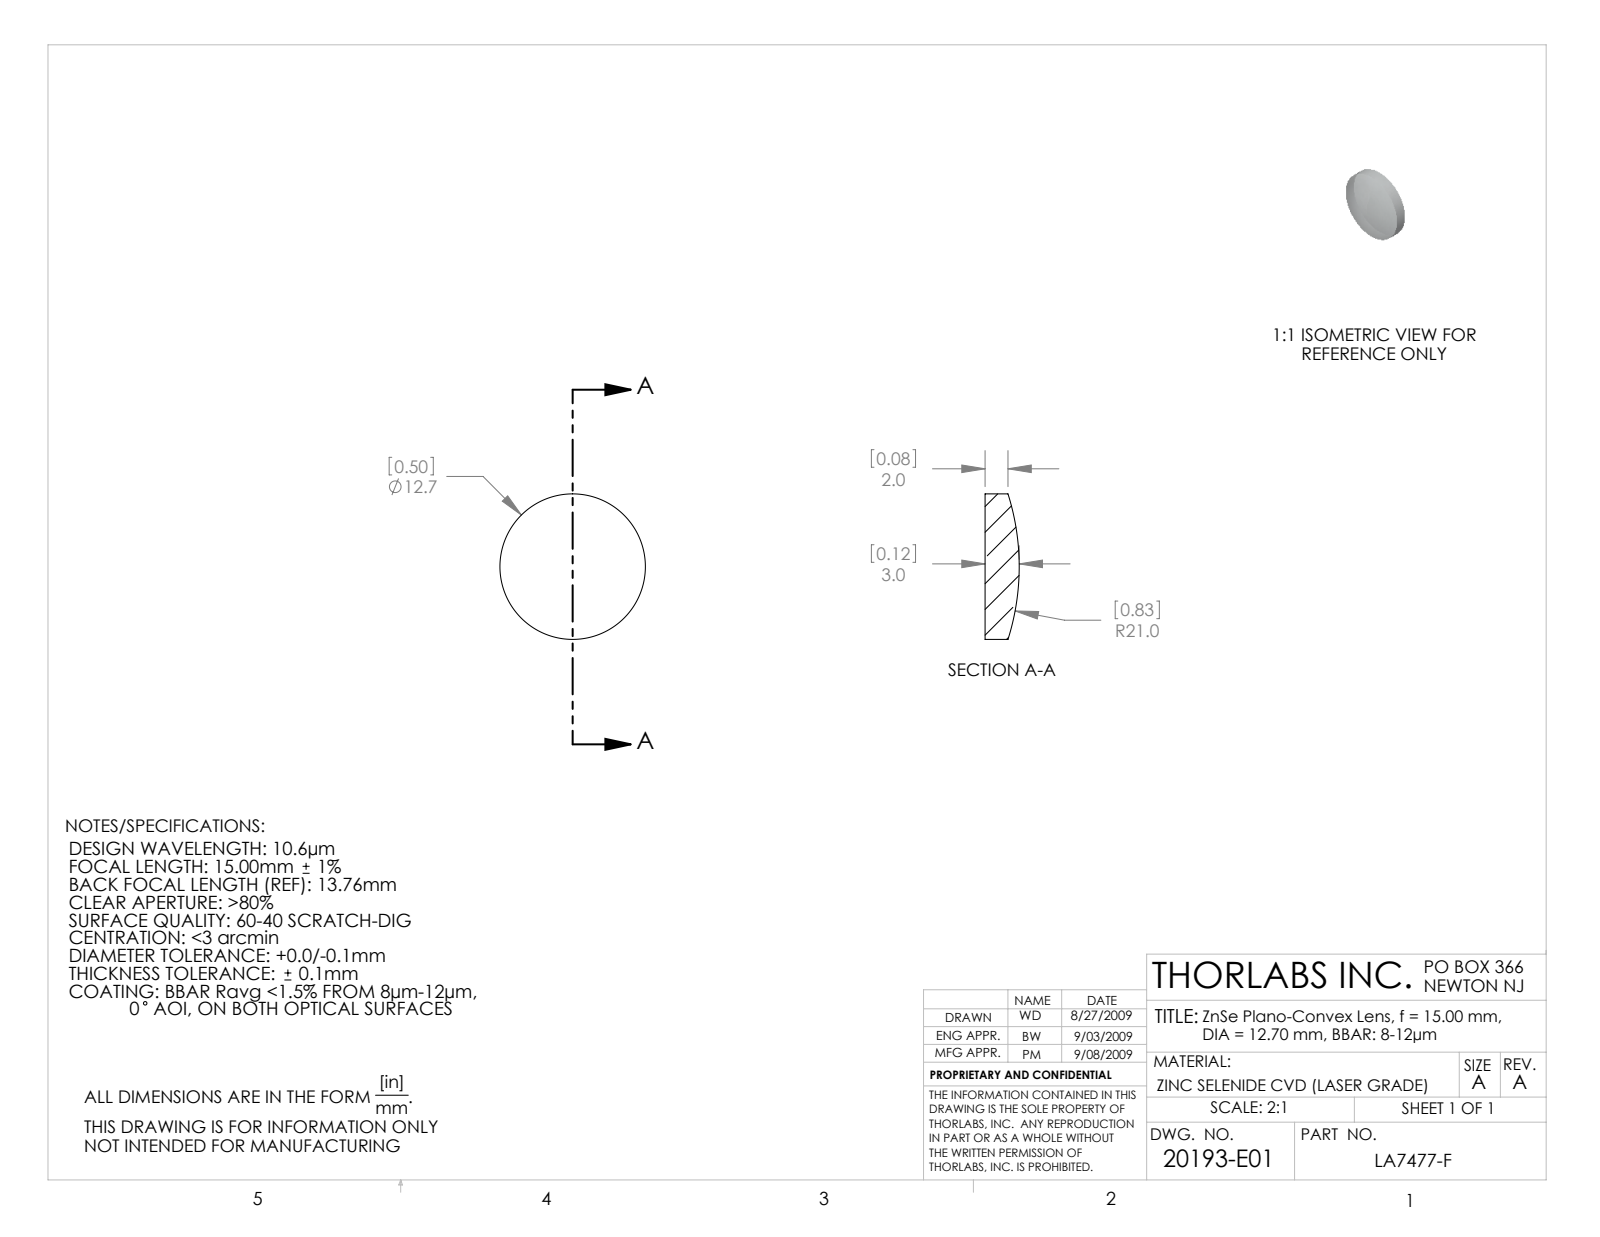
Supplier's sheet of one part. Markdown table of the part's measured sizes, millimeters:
| quantity | value |
| --- | --- |
| part name | 20193-E0W |
| STEP written by | SolidWorks 2007 (CONFIG_CONTROL_DESIGN) |
| units | millimeters |
| bodies | 1 solid, 5 faces (1 planar, 2 cylindrical, 2 other) |
| overall size | 12.7 × 12.7 × 2.98 |
| volume | 316 mm³ |
| surface area | 336 mm² |
| round bosses / shafts (diameter × count) | 12.7 × 1 |
